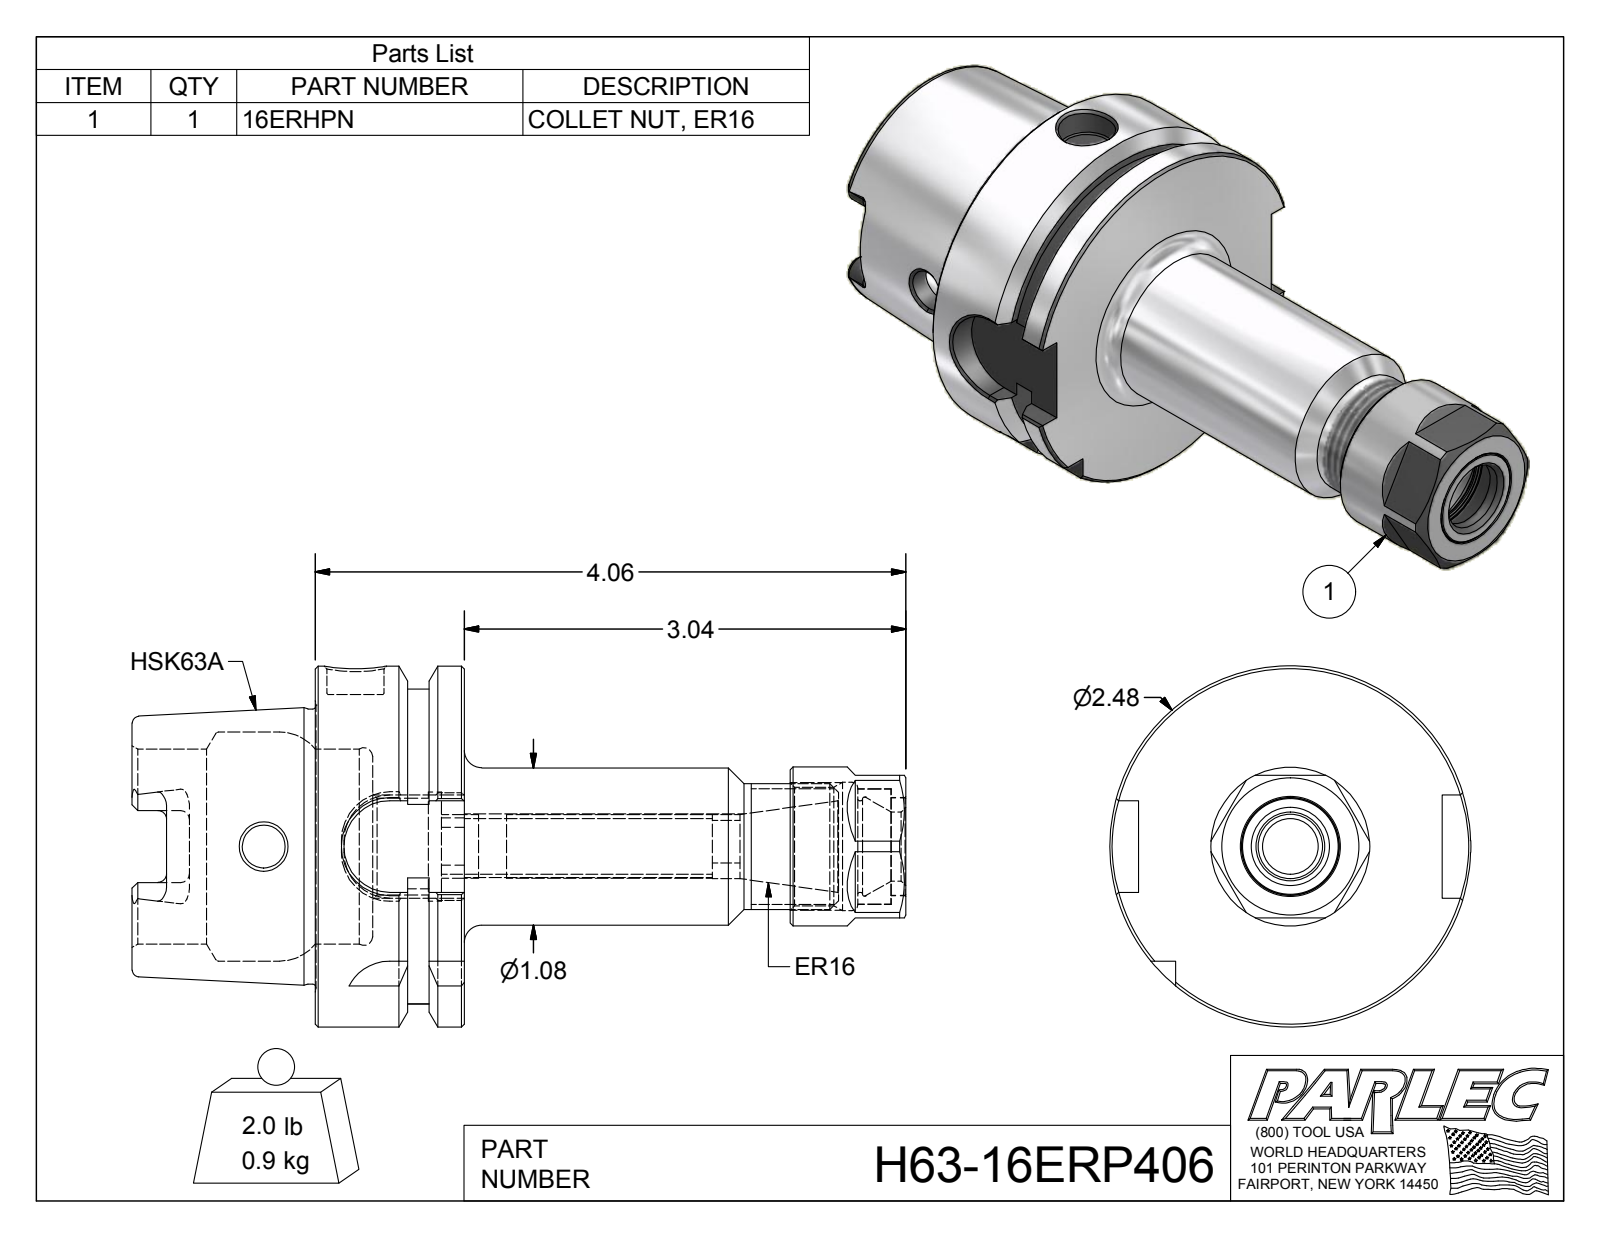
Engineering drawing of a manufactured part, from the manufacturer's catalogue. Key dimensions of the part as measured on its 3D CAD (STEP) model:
Part name (STEP PRODUCT): H63-16ERP406; H63-16ER4-1; 16ERHPN
STEP written by: Autodesk Inventor 2012 (AUTOMOTIVE_DESIGN)
Units: inches
Bodies: 3 solids, 181 faces (77 planar, 46 cylindrical, 58 other)
Overall size (bounding box): 5.32 × 2.48 × 2.48
Volume: 7.057 in³ · Surface area: 53.55 in²
Round holes (diameter × count): ⌀0.295 ×1, ⌀0.383 ×1, ⌀0.394 ×1, ⌀0.44 ×1, ⌀0.474 ×1, ⌀0.63 ×1, ⌀0.666 ×1, ⌀0.674 ×1, ⌀0.68 ×1, ⌀0.749 ×1, ⌀0.794 ×1, ⌀0.814 ×1
Round bosses / shafts (diameter × count): ⌀2.48 ×1, ⌀1.891 ×1, ⌀1.092 ×1, ⌀1.08 ×1, ⌀0.866 ×1, ⌀0.79 ×1, ⌀0.67 ×1
Partial cylindrical surfaces — rounded edges, fillets, slot ends (radius × count): R0.059 ×6, R0.113 ×4, R0.315 ×4, R0.191 ×1, R1.083 ×1
Main face-to-face distances: 1.024, 0.241, 0.389, 0.394, 0.63, 1.26, 1.654, 2.283, 2.043, 0.783
